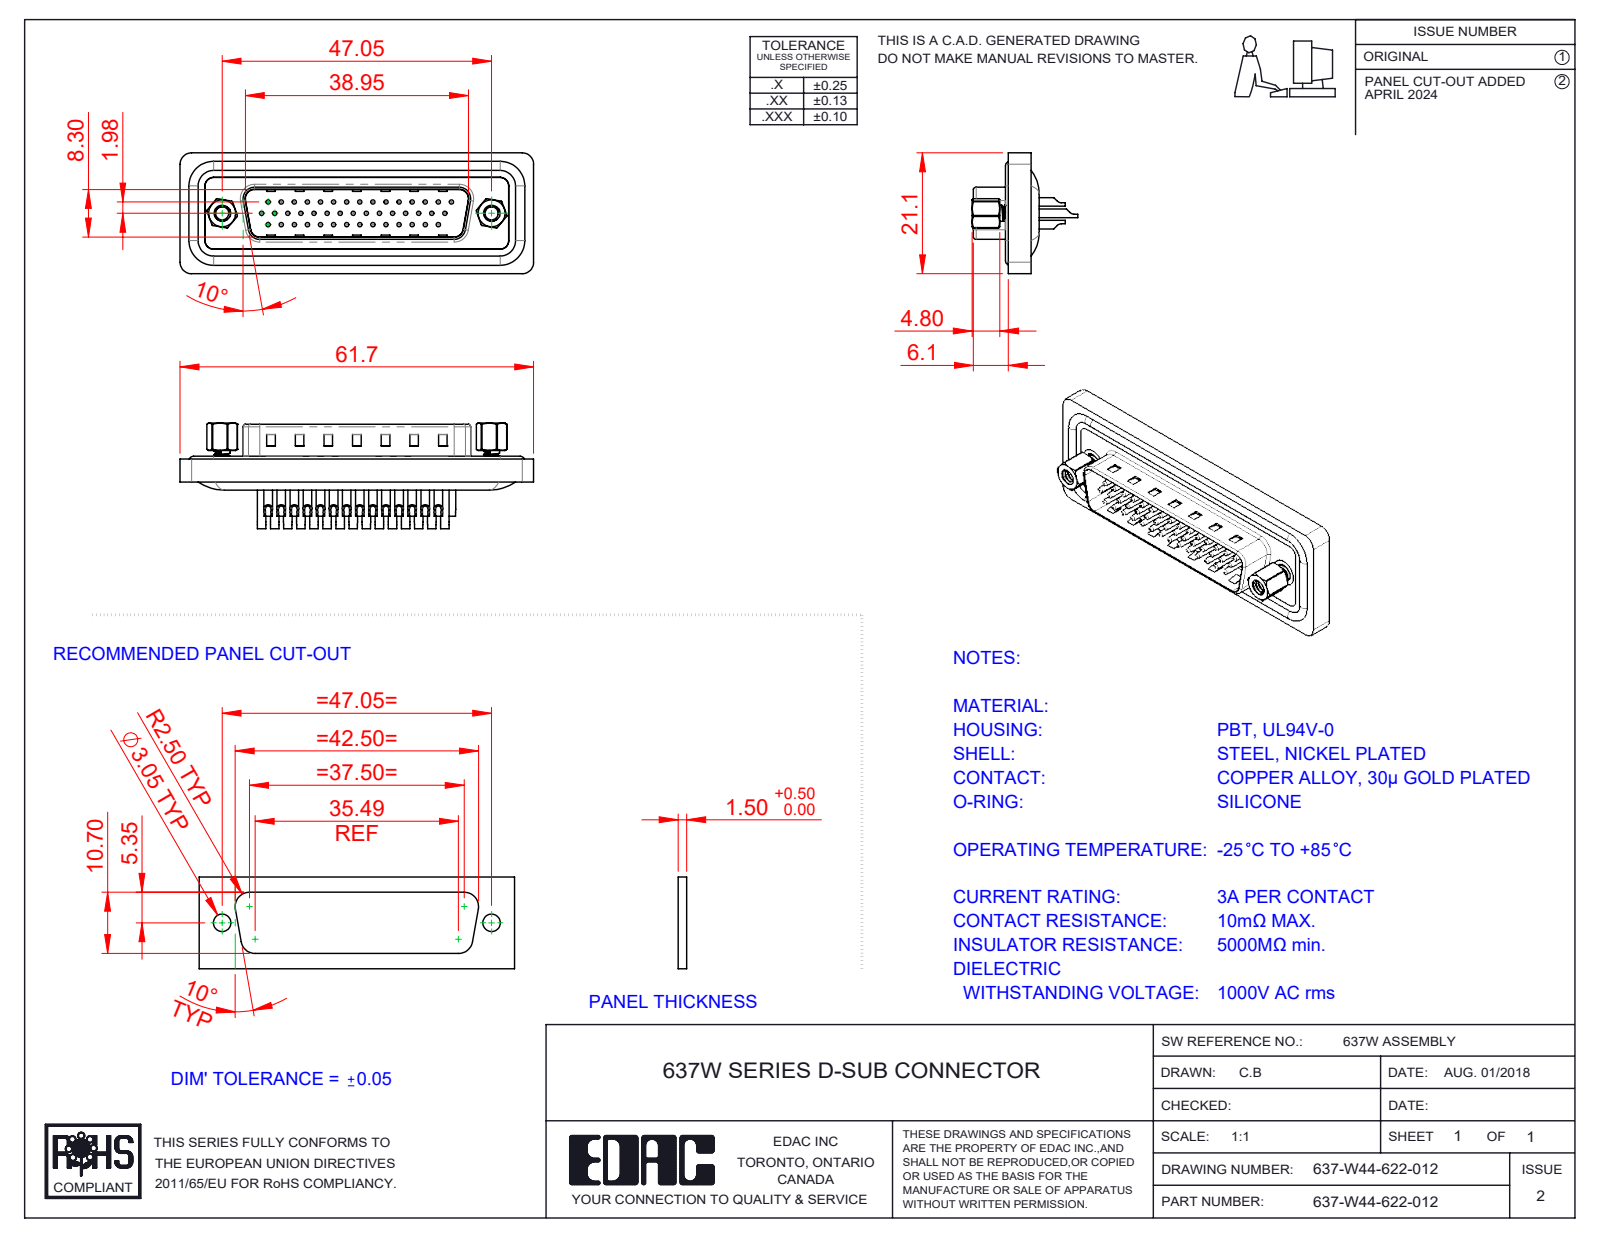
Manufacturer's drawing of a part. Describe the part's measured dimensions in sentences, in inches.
The part is named "637W Contact Row 2_22; 637W Shell_44 Contacts; 637W Waterproof Housing_44 Contacts; 637W Contact Row 3_22 (+5 more)". Its 3-D file was written by "SolidWorks 2023 (CONFIG_CONTROL_DESIGN)". It is 52 solids with 2236 faces: 601 planar, 1012 cylindrical and 623 other. Overall it measures 2.431 by 0.831 by 0.726 inches. Its volume is 0.397 cubic inches and its surface area 19.45 square inches. Round holes: 44 of diameter 0.03, 44 of diameter 0.039, 44 of diameter 0.059, 44 of diameter 0.063, 44 of diameter 0.079, 2 of diameter 0.089, 2 of diameter 0.09, 2 of diameter 0.157, 2 of diameter 0.189, 2 of diameter 0.197. Round bosses or shafts: 20 of diameter 0.059, 4 of diameter 0.063, 2 of diameter 0.193, 2 of diameter 0.11, 1 of diameter 0.197. Partial cylindrical surfaces (rounded edges, fillets, slot ends): 14 of radius 0.079, 13 of radius 0.059, 8 of radius 0.02, 6 of radius 0.106, 4 of radius 0.035, 4 of radius 0.063, 4 of radius 0.169, 3 of radius 0.039. The main face-to-face distances are 0.016, 0.063, 0.098, 0.114, 0.043, 0.222, 0.608, 0.252, 0.579, 0.03. The hole center spacings are 0.09, 0.156, 0.09, 0.18, 0.324, 0.27, 0.45, 0.59.
